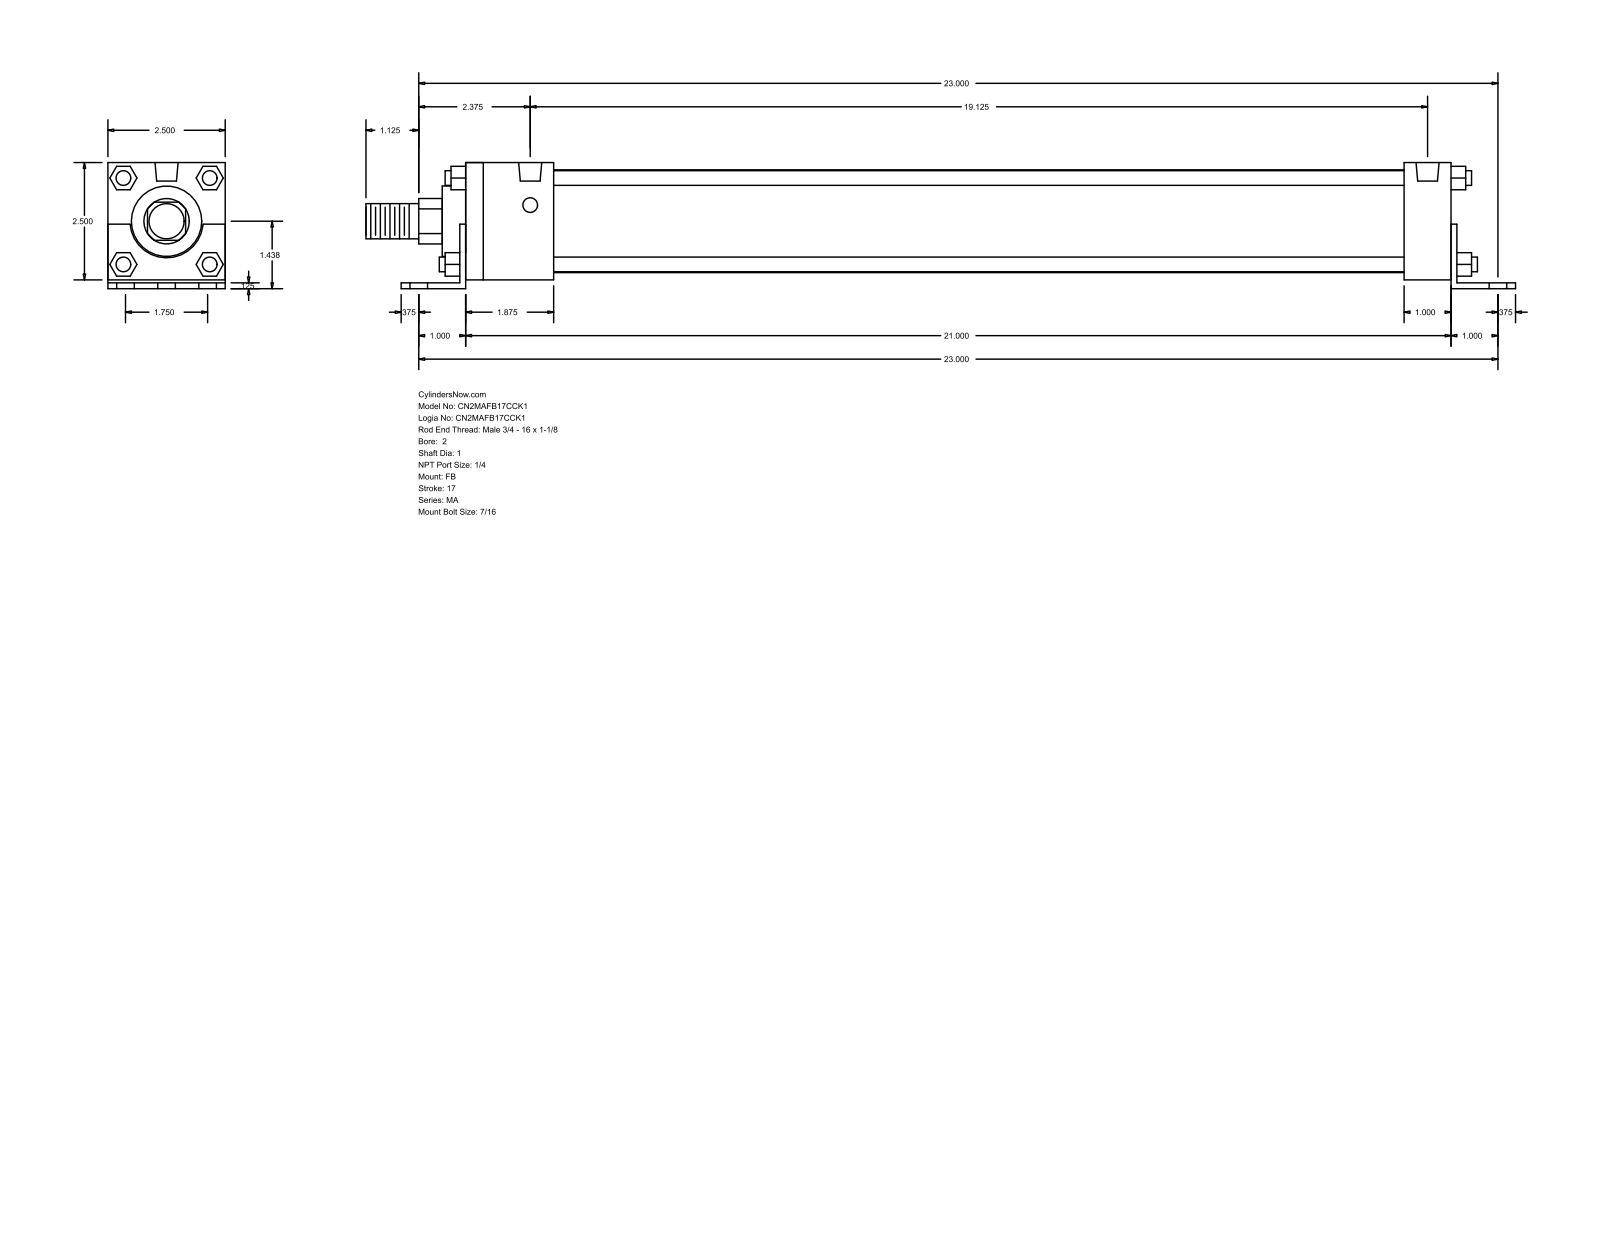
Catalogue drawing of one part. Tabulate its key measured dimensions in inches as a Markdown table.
| quantity | value |
| --- | --- |
| part name | MA_FB__0200_1 |
| STEP written by | GSSL Pune (CONFIG_CONTROL_DESIGN) |
| units | inches |
| bodies | 0 solids, 140 faces (105 planar, 35 cylindrical, 0 other) |
| overall size | 24.5 × 2.687 × 2.5 |
| round holes (diameter × count) | 0.437 × 6, 0.313 × 4, 0.492 × 2 |
| round bosses / shafts (diameter × count) | 0.313 × 4, 2.19 × 1, 1.5 × 1, 1 × 1, 0.75 × 1 |
| partial cylindrical surfaces (radius × count) | 0.484 × 1, 0.78 × 1 |
| main face-to-face distances | 2.5, 0.125, 0.187, 2.687, 0.063, 2.563, 0.5, 0.125, 21, 21.125 |
| hole center spacings | 0.875, 23.017, 23, 1.737, 1.75, 2.531, 19.125, 20.643 |
